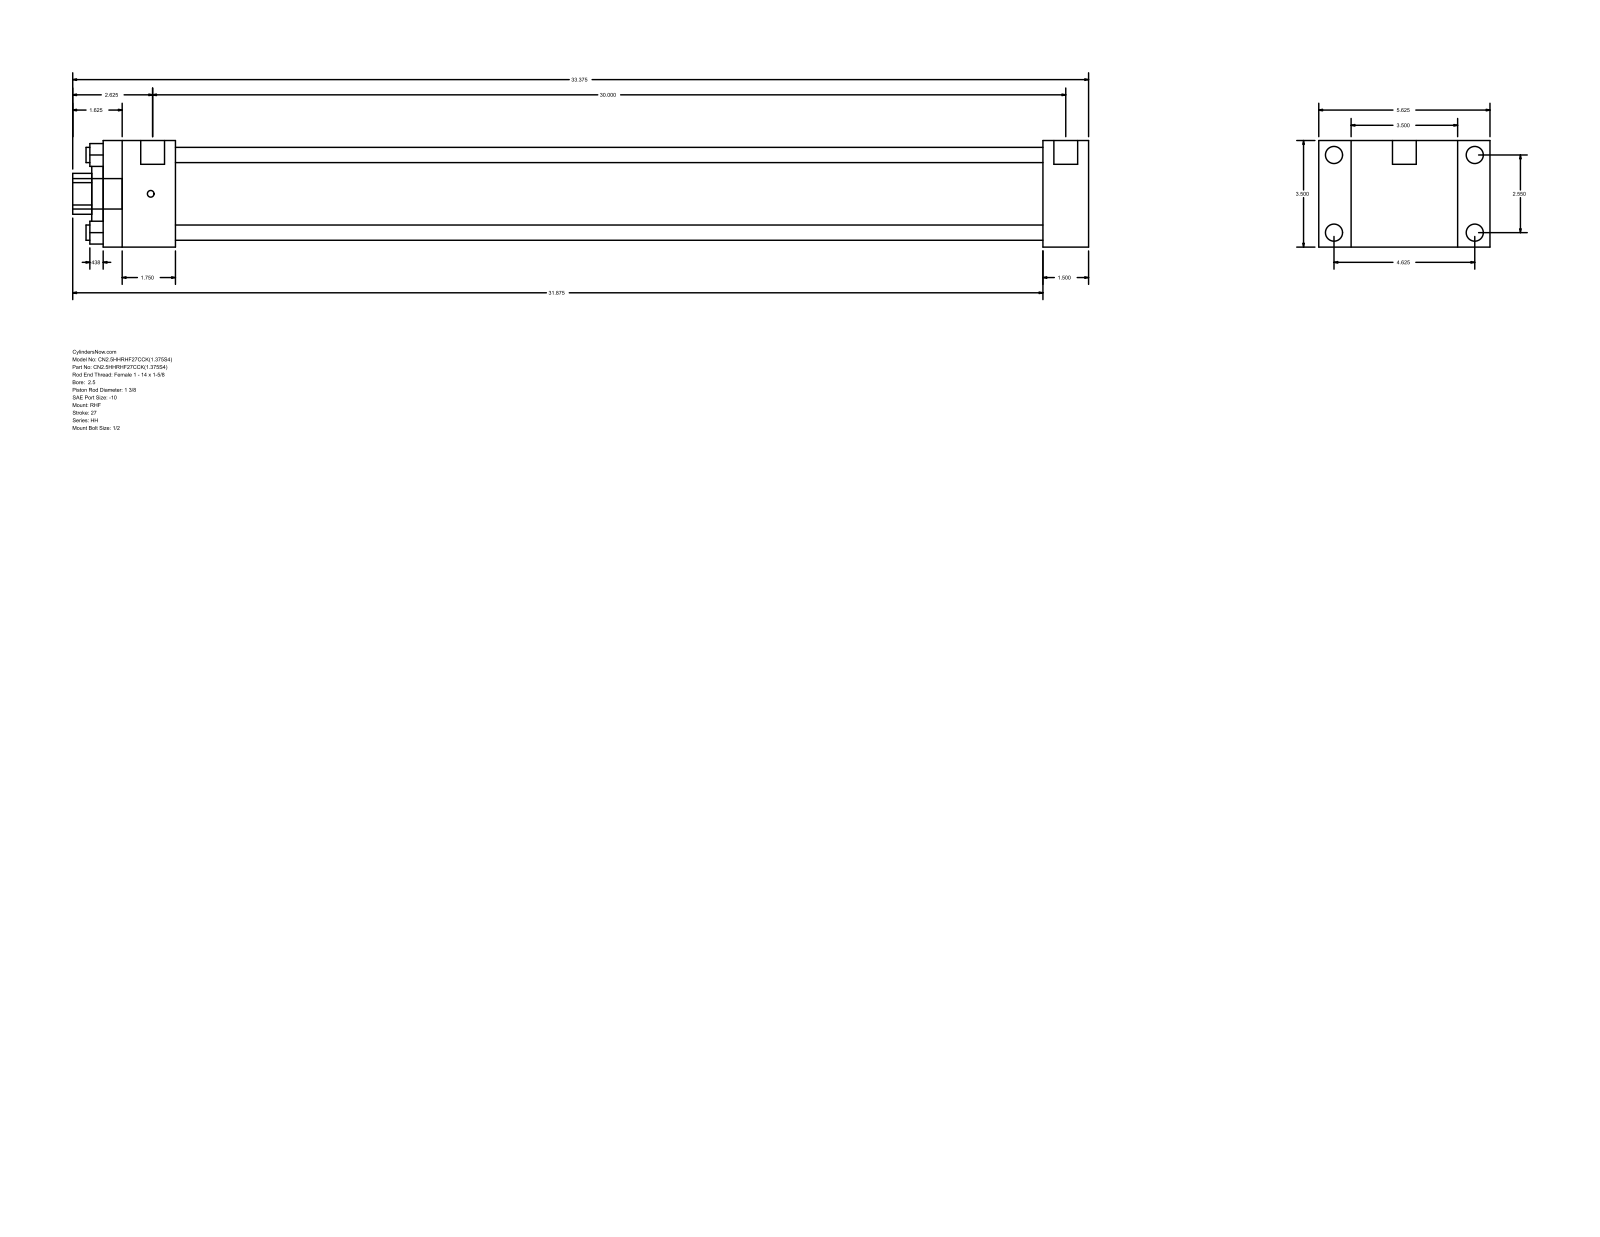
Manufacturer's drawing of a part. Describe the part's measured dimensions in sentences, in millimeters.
The part is named "HH_RHF__0250_1.375". Its 3-D file was written by "GSSL Pune (CONFIG_CONTROL_DESIGN)". It is 0 solids with 88 faces: 60 planar, 28 cylindrical and 0 other. Overall it measures 847.73 by 142.88 by 88.9 millimeters. Round holes: 4 of diameter 12.7, 1 of diameter 34.92, 1 of diameter 50.8, 1 of diameter 73.03. Round bosses or shafts: 4 of diameter 14.3, 4 of diameter 5.56, 2 of diameter 19.84, 1 of diameter 25.4. Partial cylindrical surfaces (rounded edges, fillets, slot ends): 1 of radius 17.06. The main face-to-face distances are 88.9, 38.11, 26.99, 115.89, 784.22, 822.33, 142.88, 60.32, 723.9, 762.01. The hole center spacings are 45.79, 64.76, 91.58.
